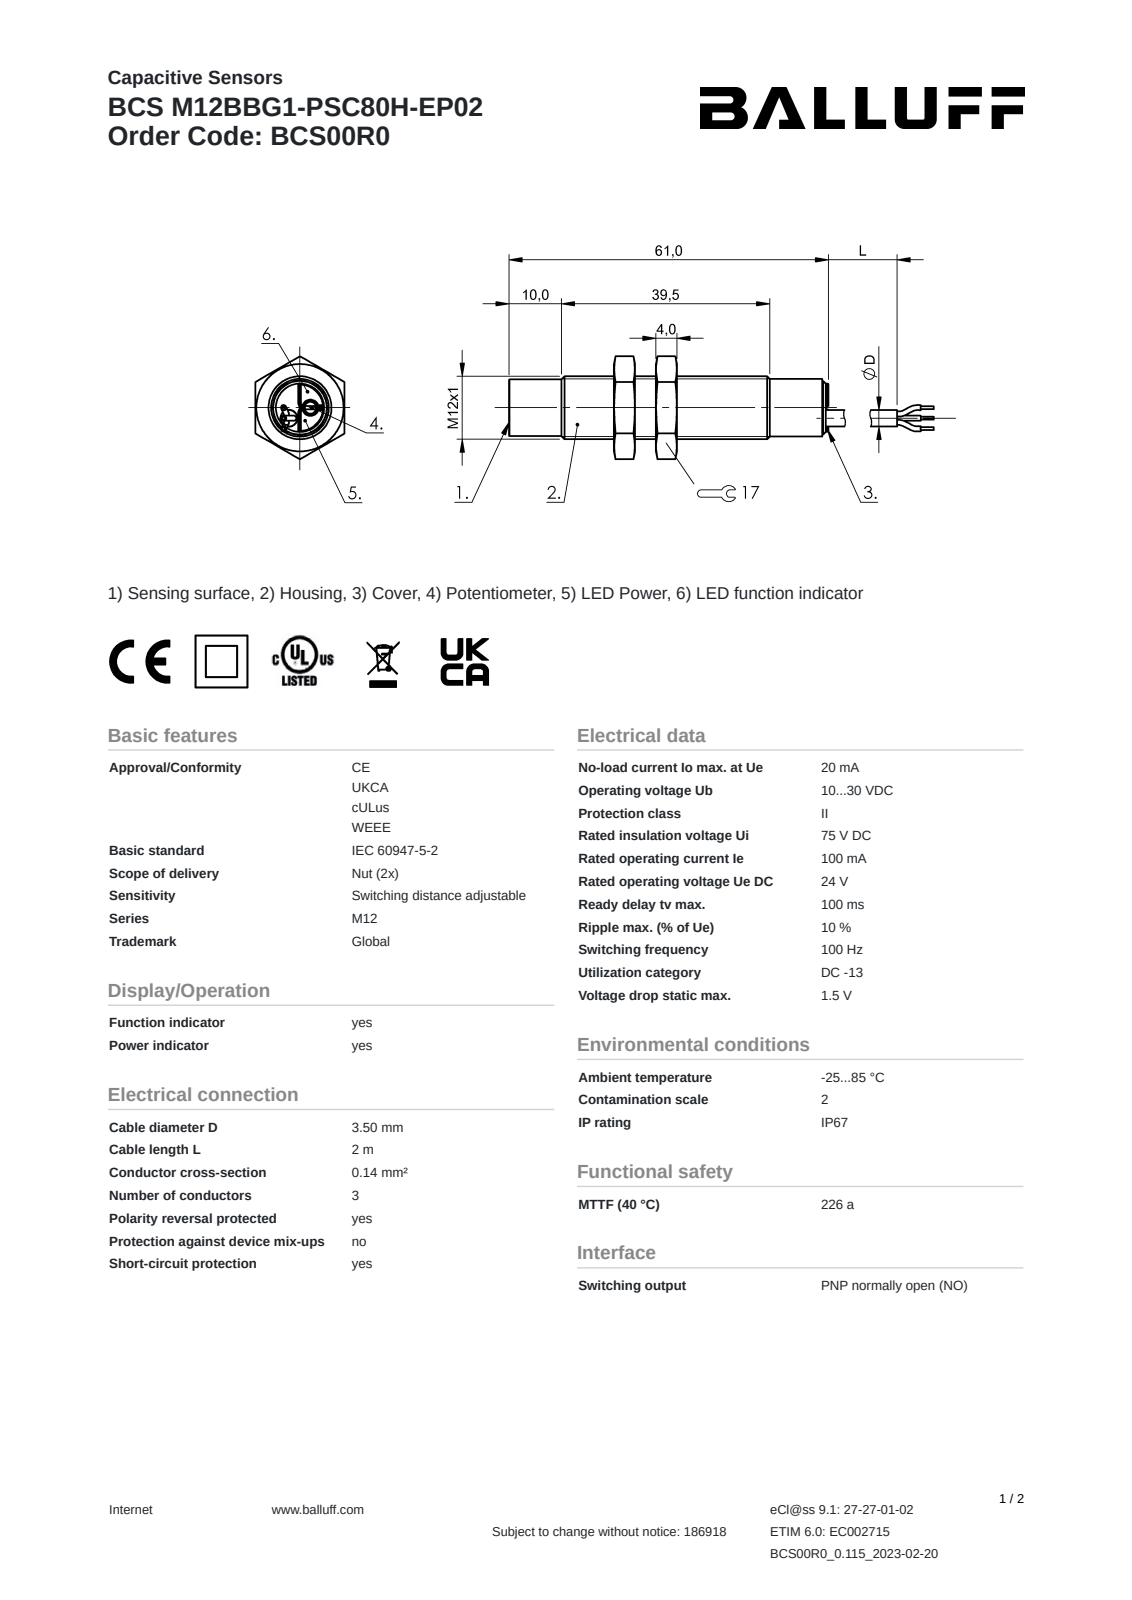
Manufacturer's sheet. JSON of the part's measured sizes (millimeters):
{"part_name": "BCS00R0", "step_written_by": "SolidWorks 2021 (AUTOMOTIVE_DESIGN)", "units": "millimeters", "bodies": {"solids": 3, "faces": 80, "planar": 36, "cylindrical": 13, "other": 31}, "overall_size": [70.2, 19.6, 17], "volume_mm3": 7490, "surface_area_mm2": 3756, "round_holes": [[2.8, 1], [10.9, 1]], "round_bosses_or_shafts": [[12, 1], [10.5, 1], [10.4, 1], [10.2, 1], [2.4, 1]], "partial_cylinders_radius": [[0.3, 1], [0.5, 1], [5, 1]], "face_to_face_distances": [4, 6, 17, 10, 2, 16.7, 20.7, 26.7, 22.7, 33.6], "hole_center_spacings": [2.5]}
